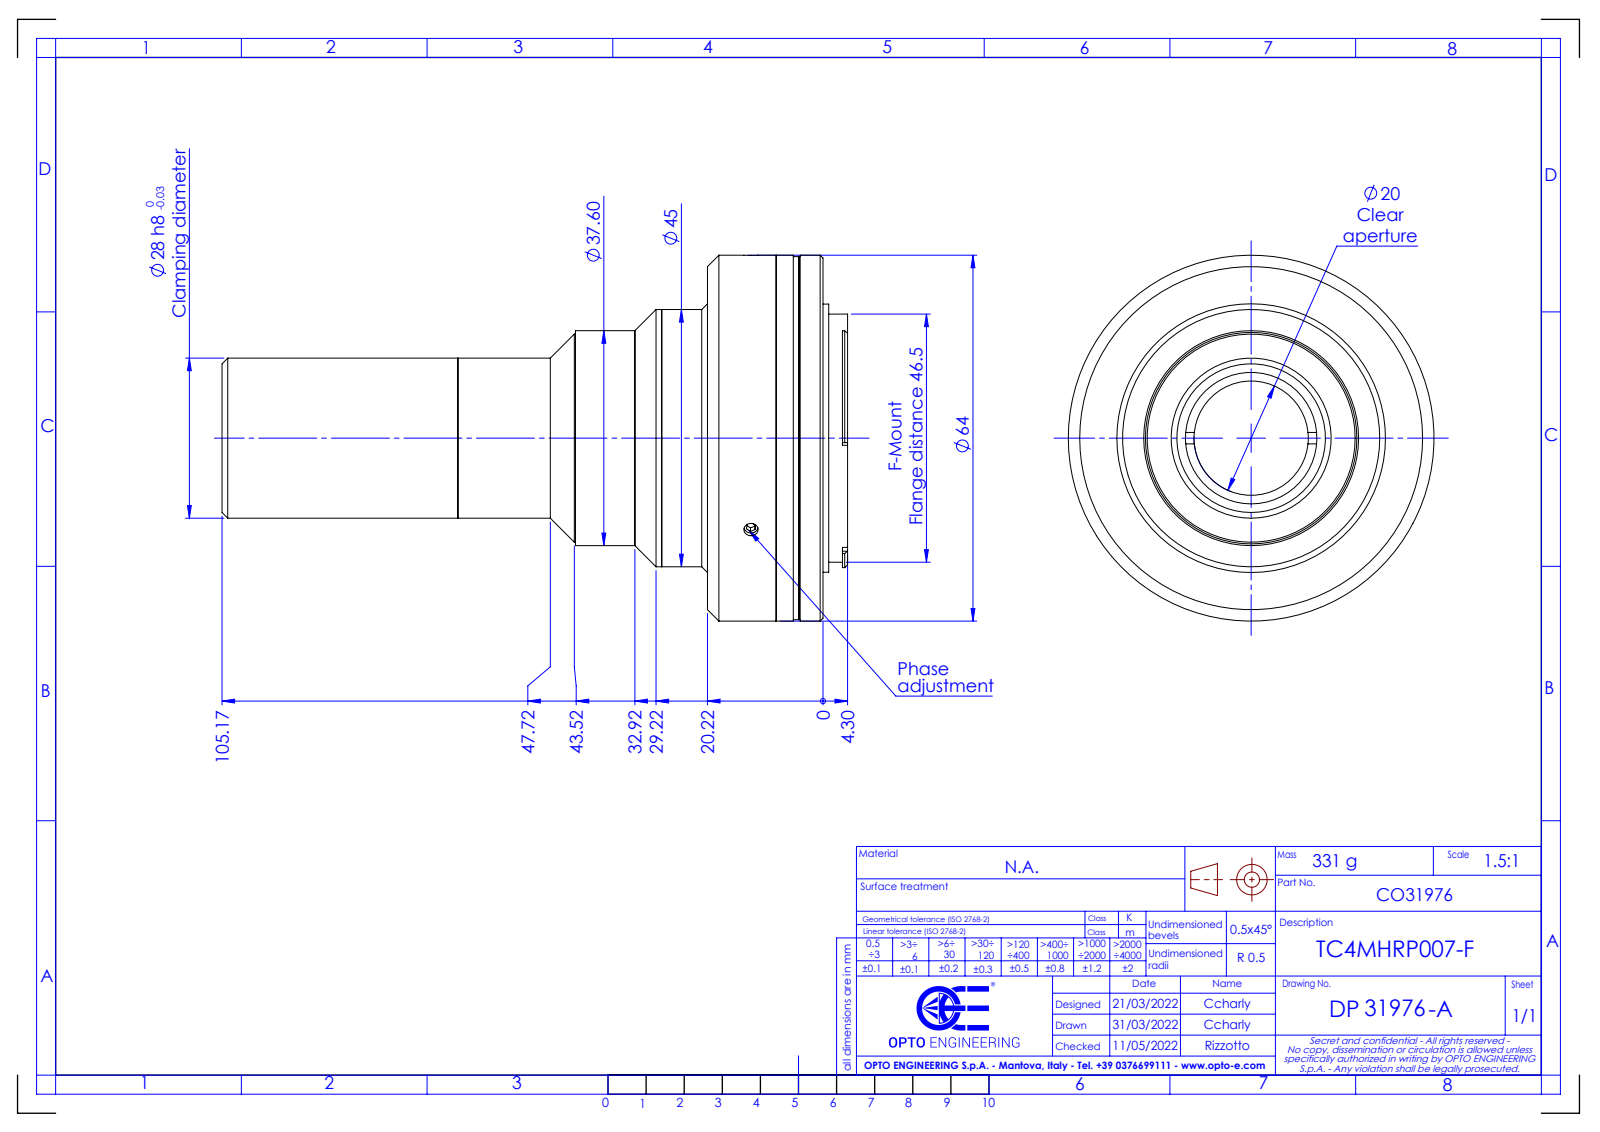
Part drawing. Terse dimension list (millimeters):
name: DP31976-A_TC4MHRP007-F
written by: SolidWorks 2021 (CONFIG_CONTROL_DESIGN)
unit: mm
bodies: 0 solids, 128 faces (49 planar, 53 cylindrical, 26 other)
size: 109.47 × 64 × 64
holes: 3× ⌀2.5, 1× ⌀20, 1× ⌀23, 1× ⌀35, 1× ⌀42
bosses: 1× ⌀64, 1× ⌀63.5, 1× ⌀46.9, 1× ⌀45, 1× ⌀43.4, 1× ⌀37.6, 1× ⌀36.4, 1× ⌀28
rounds: 6× R0.5, 2× R1.15, 1× R22.65
face distances: 18.72, 10.52, 8.2, 1.5, 13.52, 3, 5.2, 12.02, 15.02, 20.22
